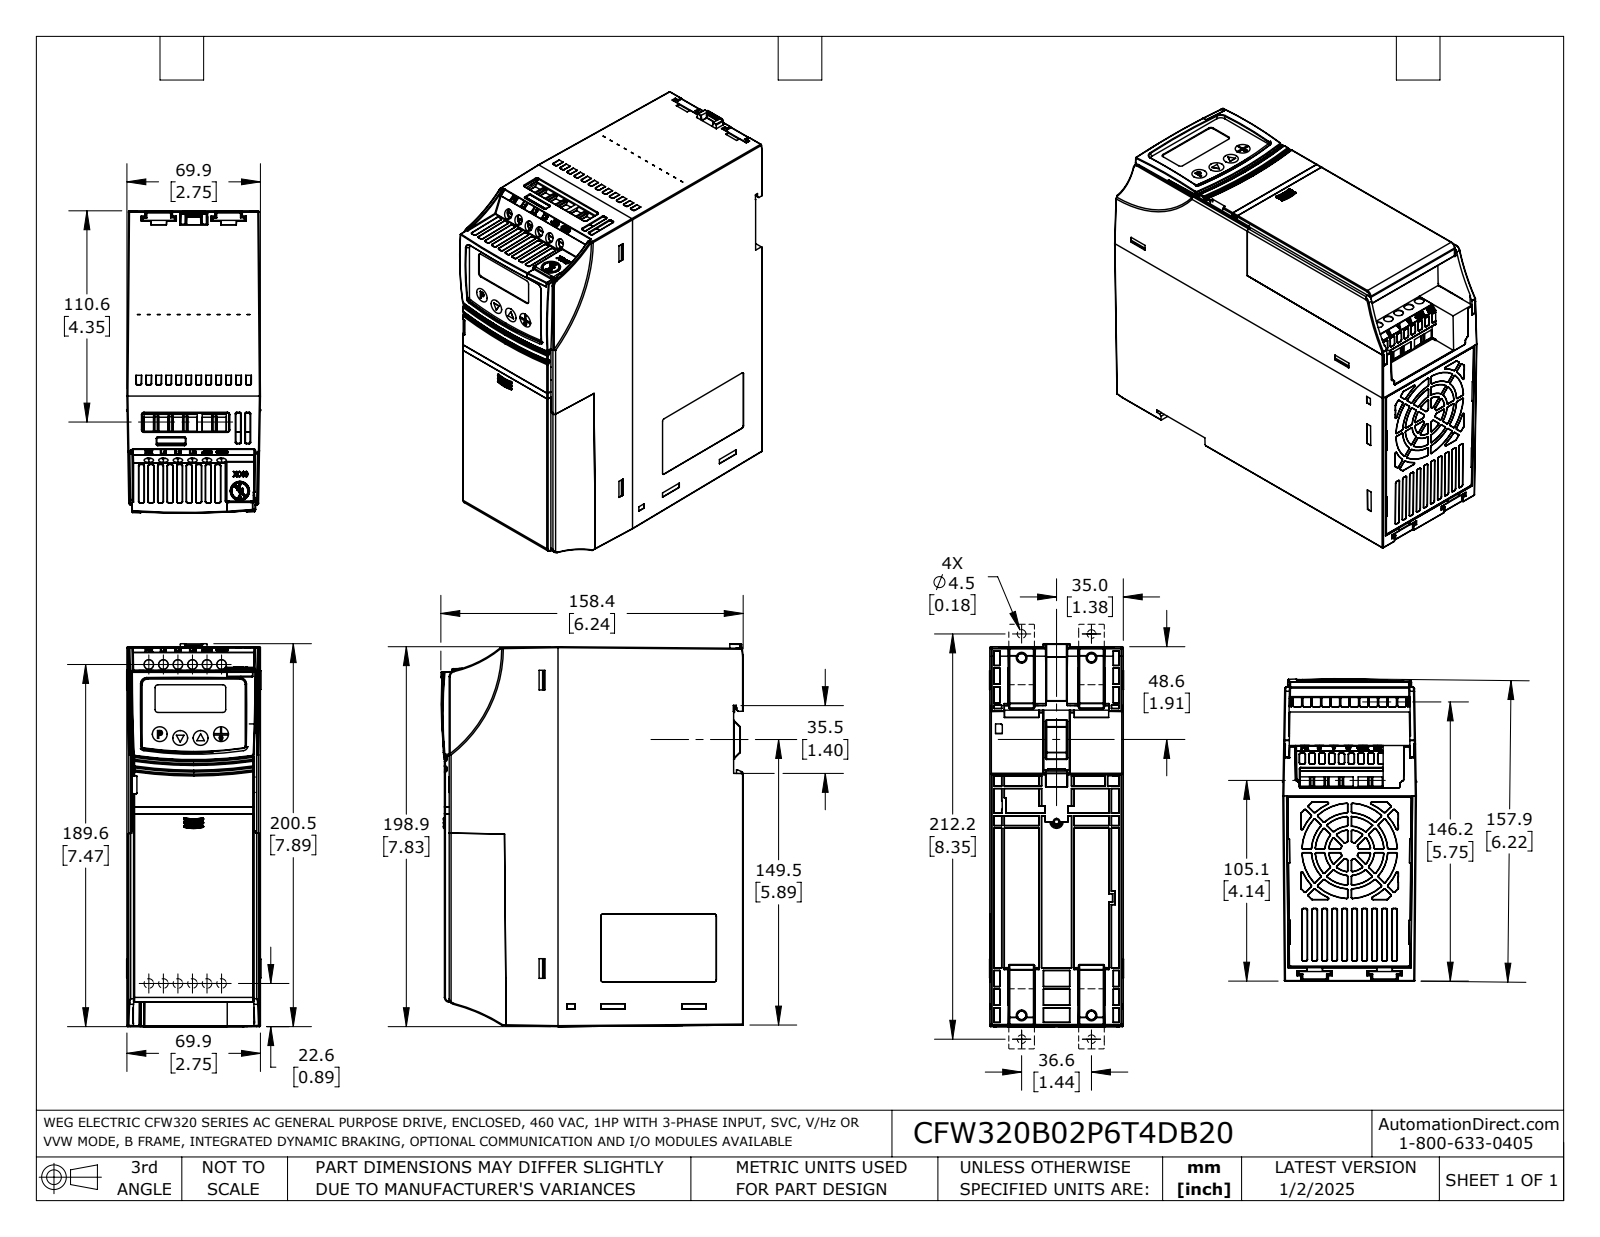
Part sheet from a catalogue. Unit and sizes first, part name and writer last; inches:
Units: inches
Overall size (bounding box): 7.894 × 6.235 × 2.764
Round holes (diameter × count): ⌀0.193 ×6
Partial cylindrical surfaces — rounded edges, fillets, slot ends (radius × count): R0.012 ×355, R0.02 ×181, R0.039 ×14, R0.03 ×7, R0.118 ×5, R0.01 ×2, R0.109 ×2, R0.098 ×1
Main face-to-face distances: 0.209, 0.098, 0.1, 5.826, 5.728, 0.211, 5.939, 6.037, 7.5, 0.039
Hole centre spacings: 0.3, 0.6, 0.9, 1.2, 1.5
Volume: 24.51 in³ · Surface area: 385.1 in²
Bodies: 5 solids, 3984 faces (1907 planar, 899 cylindrical, 1178 other)
Part name (STEP PRODUCT): CFW320B02P6T4DB20
STEP written by: SolidWorks 2021 (AUTOMOTIVE_DESIGN)
